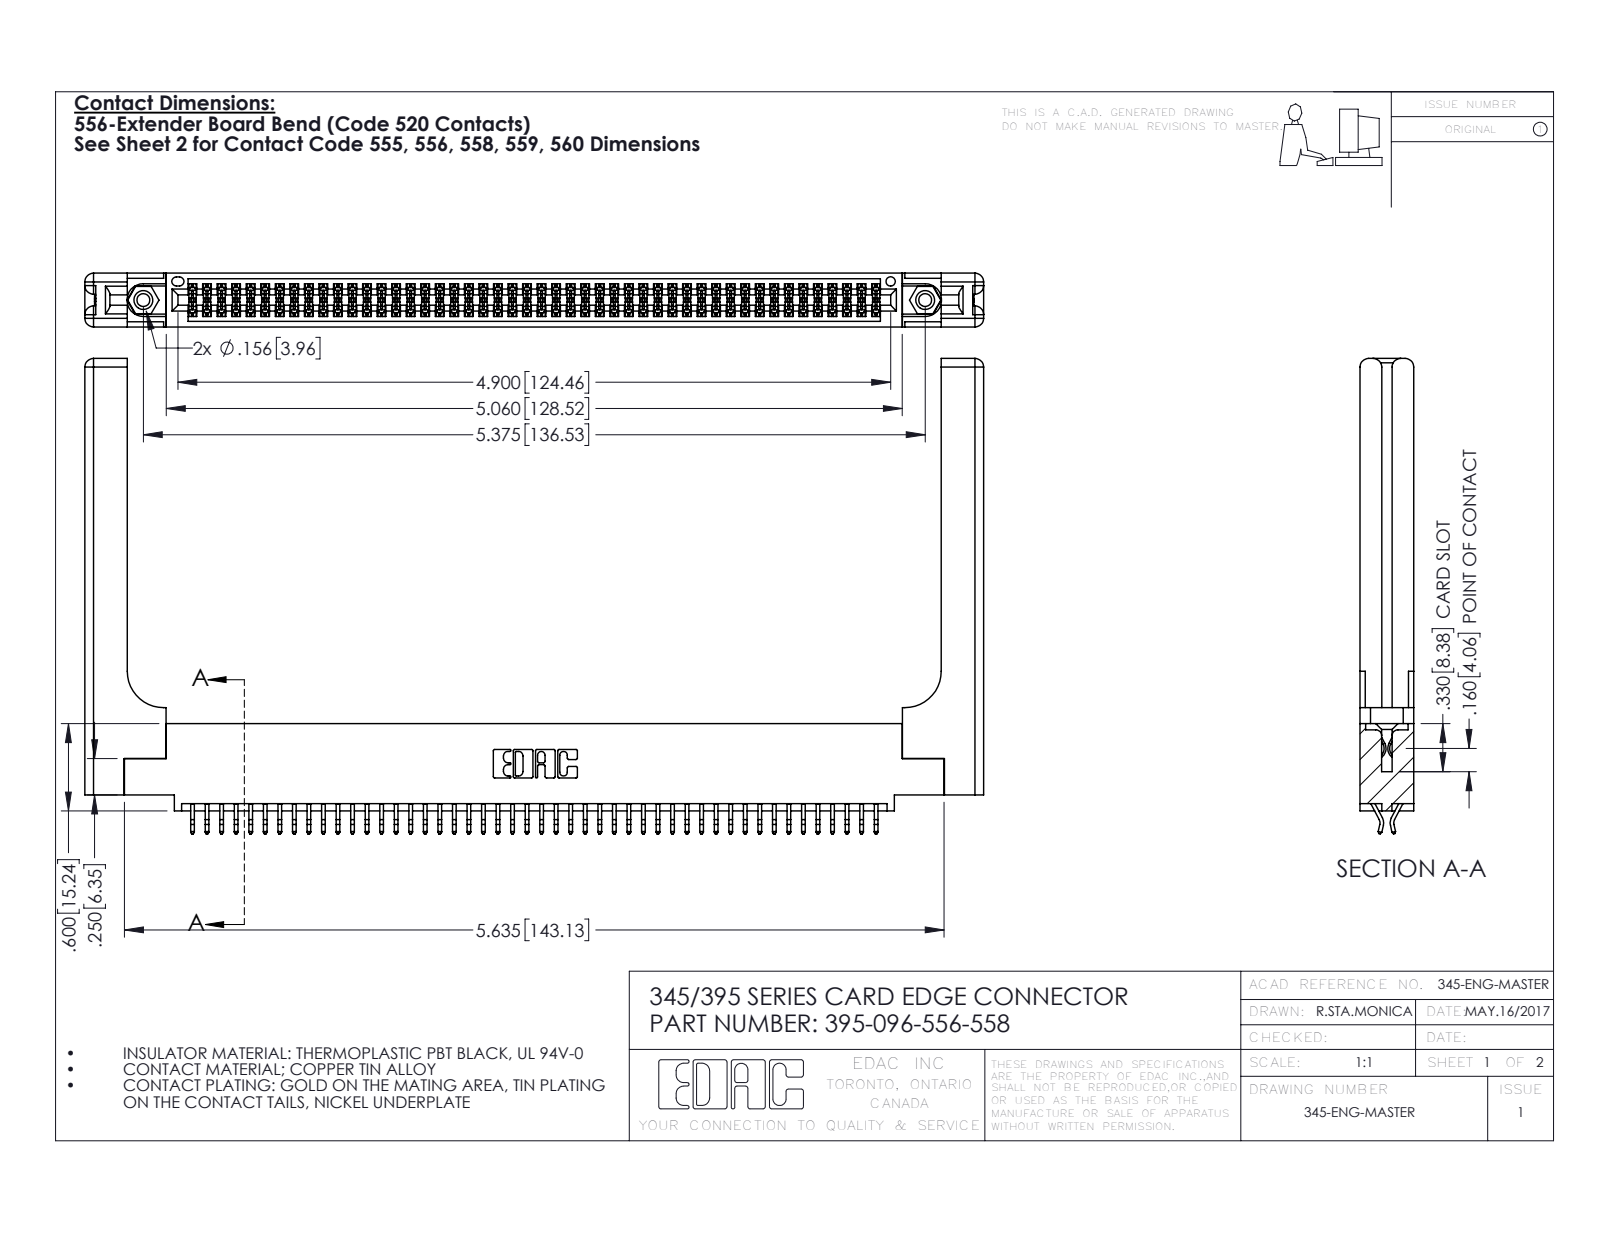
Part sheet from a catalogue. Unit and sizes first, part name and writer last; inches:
Units: inches
Overall size (bounding box): 6.179 × 3.267 × 0.37
Round holes (diameter × count): ⌀0.089 ×2, ⌀0.125 ×2, ⌀0.156 ×2, ⌀0.064 ×1
Round bosses / shafts (diameter × count): ⌀0.155 ×2
Partial cylindrical surfaces — rounded edges, fillets, slot ends (radius × count): R0.006 ×144, R0.01 ×22, R0.06 ×16, R0.007 ×6, R0.031 ×6, R0.026 ×3, R0.01 ×2, R0.014 ×2
Main face-to-face distances: 0.072, 0.37, 0.298, 0.025, 0.098, 0.272, 0.2, 0.225, 0.148, 0.15
Hole centre spacings: 0.27, 5.139, 5.375
Volume: 1.446 in³ · Surface area: 42.92 in²
Bodies: 101 solids, 5762 faces (3784 planar, 1918 cylindrical, 60 other)
Part name (STEP PRODUCT): 345-250-001_345-250-001-102; 345 Part_0.110 Offset - 0.156 Dia-TH; 345-220-058_345-220-058; 395-096-556-558 (+1 more)
STEP written by: SolidWorks 2016 (CONFIG_CONTROL_DESIGN)
